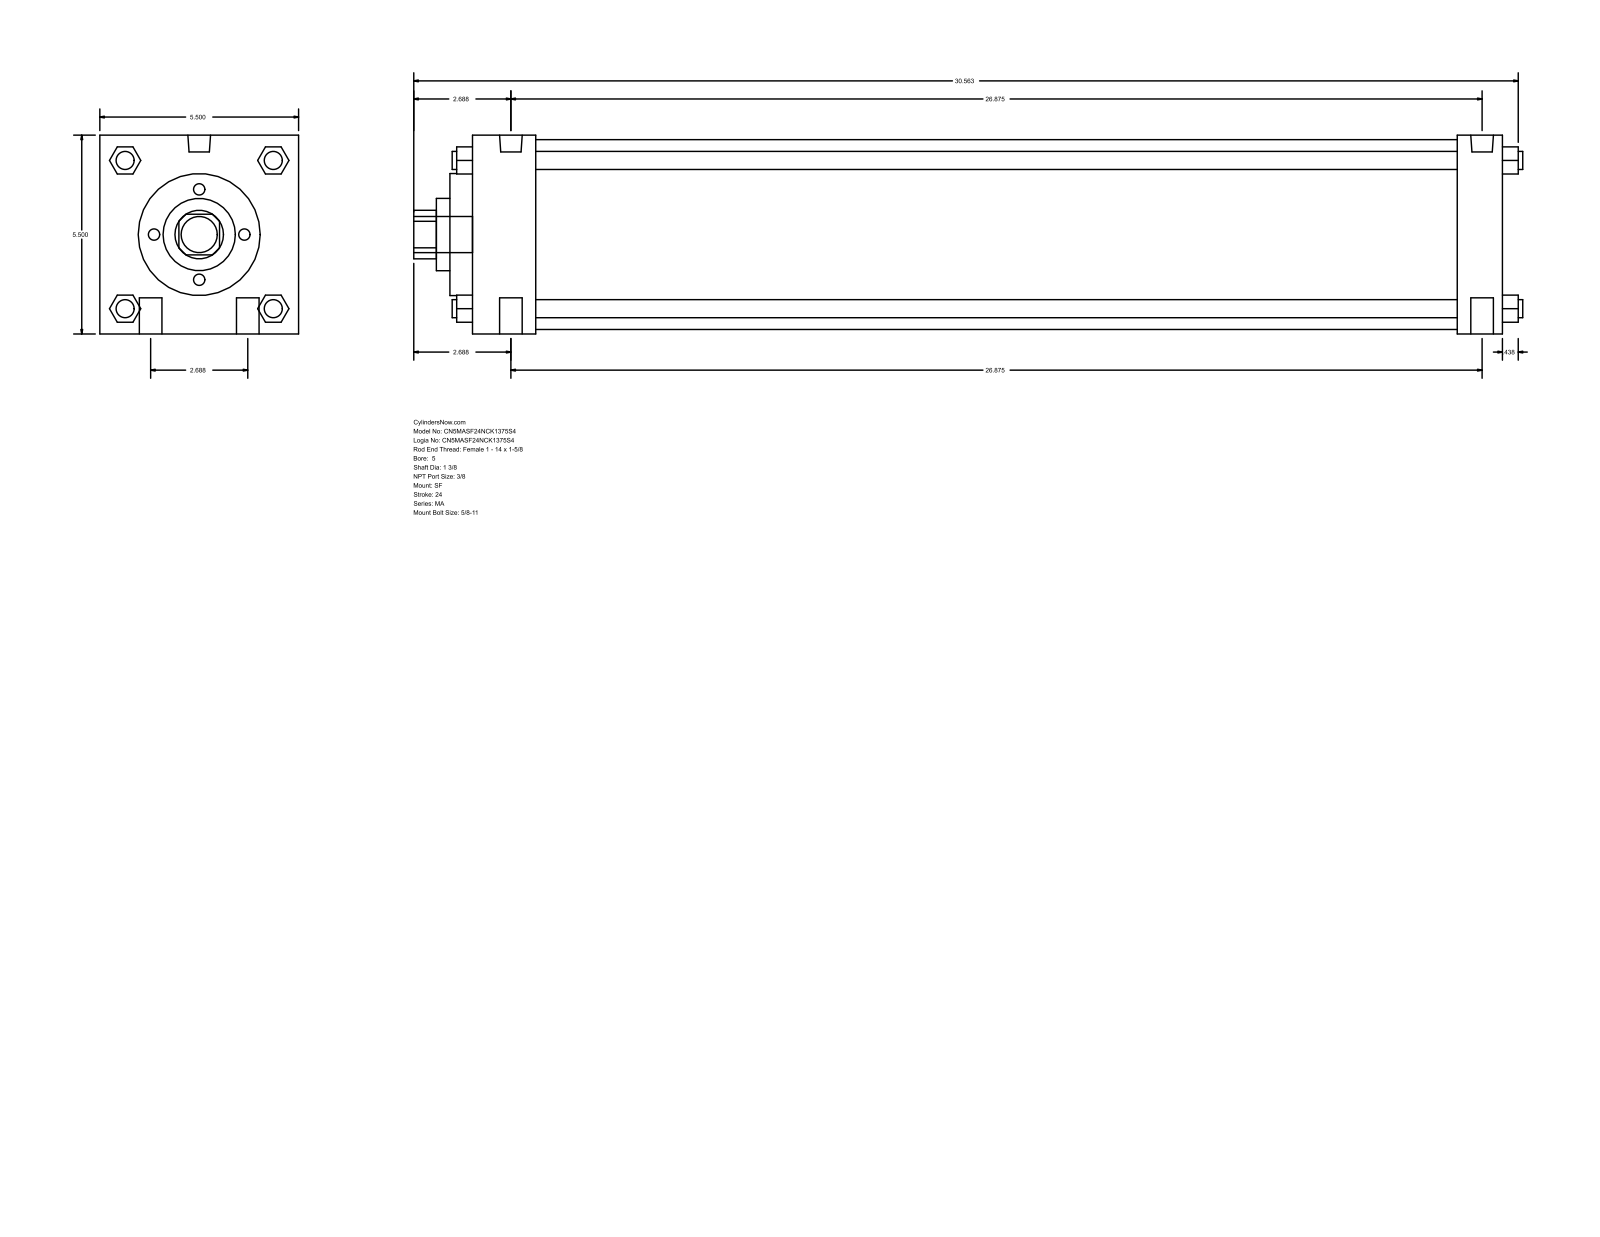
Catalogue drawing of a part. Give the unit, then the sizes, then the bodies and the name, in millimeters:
Units: millimetres
Overall size (bounding box): 779.46 × 139.7 × 139.7
Round holes (diameter × count): ⌀34.92 ×1, ⌀50.8 ×1, ⌀85.72 ×1, ⌀133.35 ×1
Round bosses / shafts (diameter × count): ⌀15.88 ×4, ⌀12.7 ×4, ⌀15.93 ×2, ⌀11.11 ×2, ⌀25.4 ×1
Partial cylindrical surfaces — rounded edges, fillets, slot ends (radius × count): R17.06 ×1
Main face-to-face distances: 139.7, 723.9, 44.45, 692.15, 647.7, 679.45, 31.75, 15.87, 60.32, 708.02
Bodies: 0 solids, 126 faces (95 planar, 31 cylindrical, 0 other)
Part name (STEP PRODUCT): MA_SF__0500_1.375
STEP written by: GSSL Pune (CONFIG_CONTROL_DESIGN)
